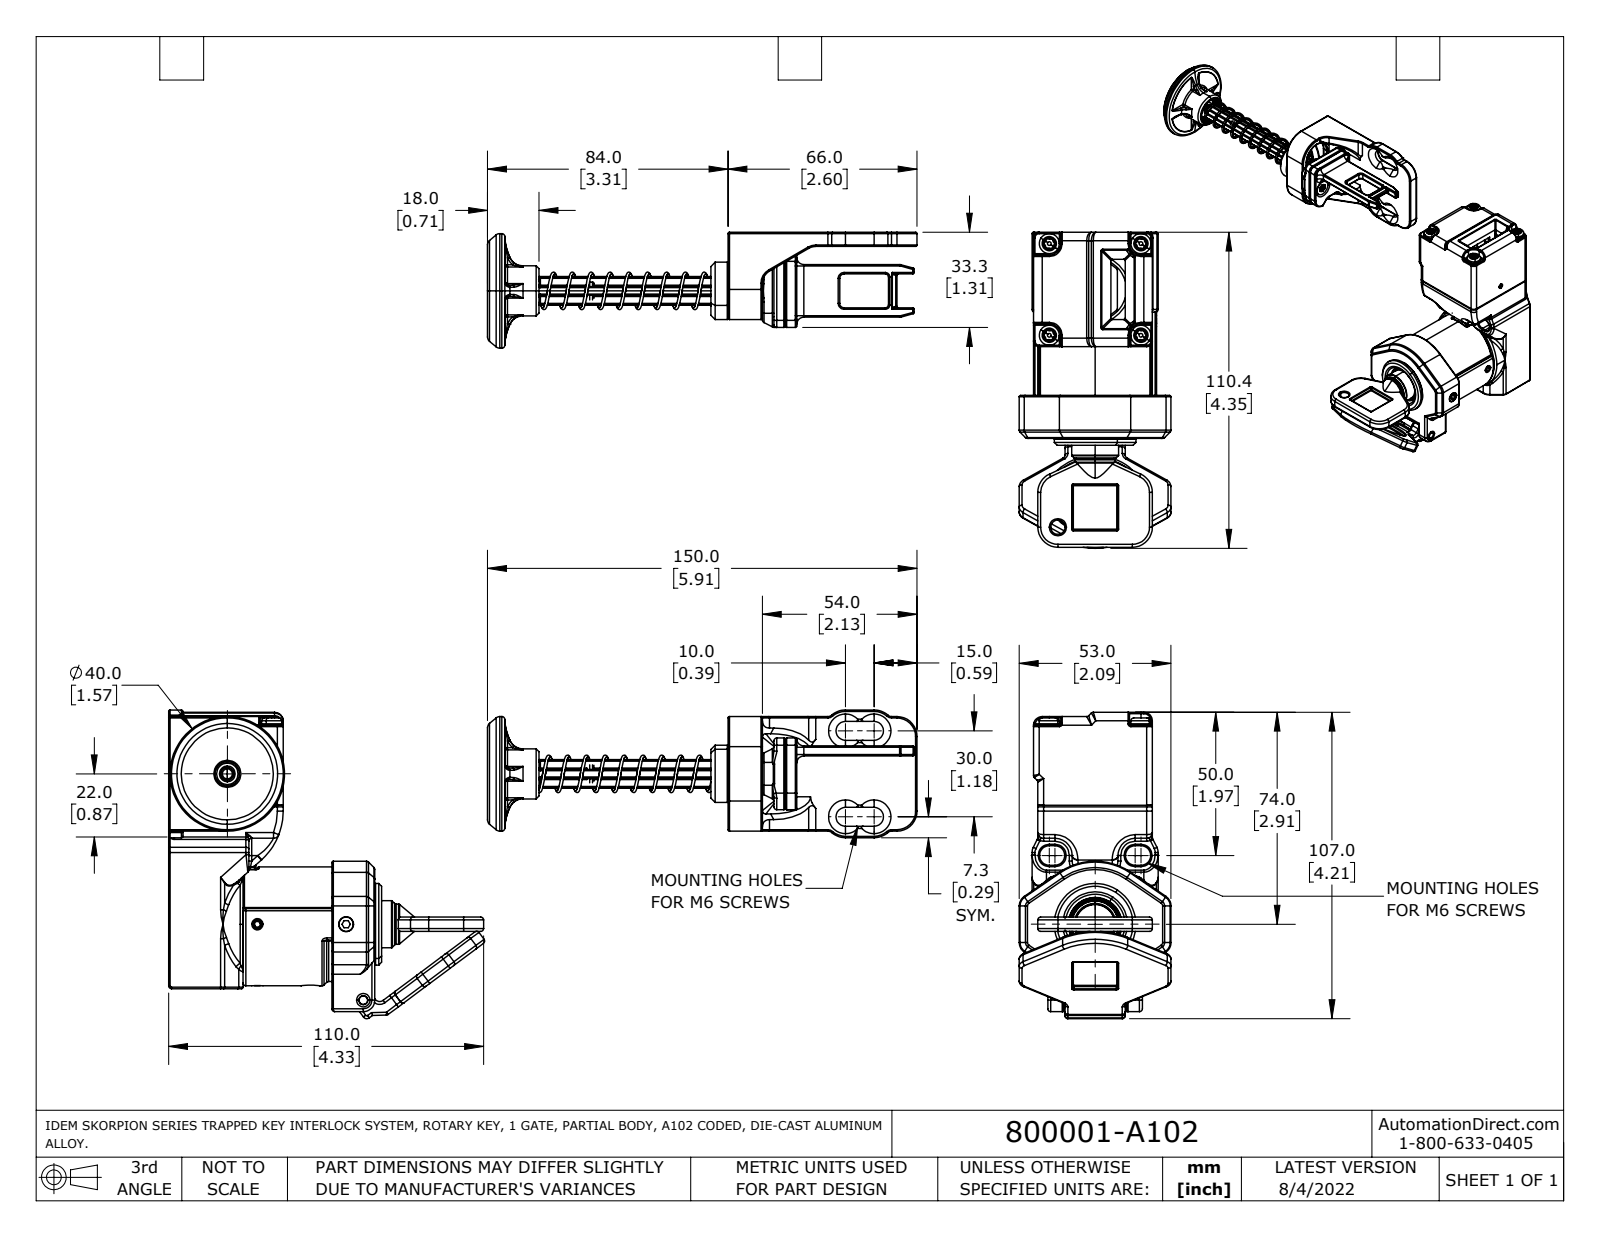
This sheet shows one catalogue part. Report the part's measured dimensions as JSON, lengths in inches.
{"part_name": "800001-CS-A101; 800001-A101_2; 800001-A101_1", "step_written_by": "SolidWorks 2021 (AUTOMOTIVE_DESIGN)", "units": "inches", "bodies": {"solids": 5, "faces": 3408, "planar": 768, "cylindrical": 1328, "other": 1312}, "overall_size": [9.397, 4.345, 4.243], "volume_in3": 9.893, "surface_area_in2": 141.4, "round_holes": [[0.13, 6], [0.138, 6], [0.157, 6], [0.165, 5], [0.177, 4], [0.197, 3], [0.087, 2], [0.098, 2], [0.12, 2], [0.209, 2], [0.315, 2], [0.079, 1]], "round_bosses_or_shafts": [[0.051, 8], [0.138, 5], [0.276, 4], [0.118, 4], [1.575, 2], [0.394, 2], [0.307, 2], [0.291, 2]], "partial_cylinders_radius": [[0.02, 474], [0.039, 176], [0.079, 32], [0.012, 28], [0.031, 18], [0.157, 16], [0.118, 13], [0.059, 8]], "face_to_face_distances": [0.197, 0.118, 0.079, 1.575, 1.654, 1.378, 1.445, 0.13, 0.256, 1.634], "hole_center_spacings": [0.891, 1.26, 1.398, 0.28, 0.66, 0.704, 0.822, 0.824]}
